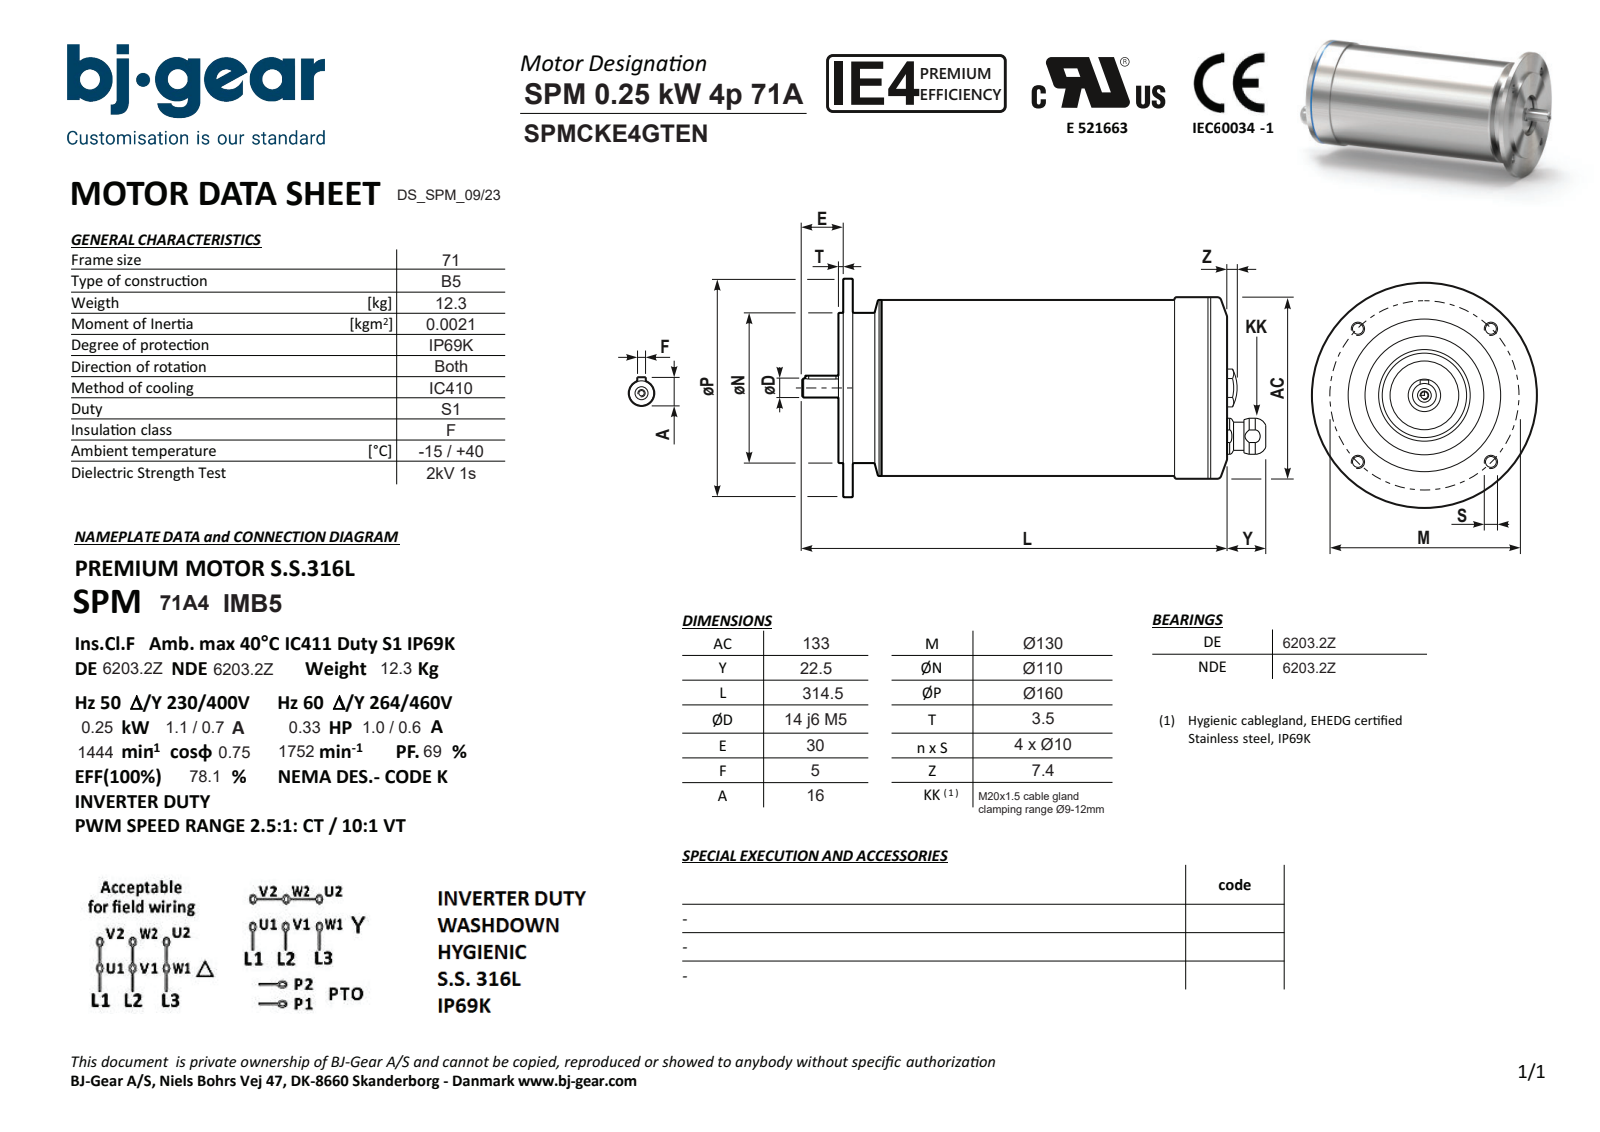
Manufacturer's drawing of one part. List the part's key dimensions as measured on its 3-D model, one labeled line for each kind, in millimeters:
Part name (STEP PRODUCT): SPMCKE4GTENN4KSA1-N---NNN
STEP written by: Solid Edge (AUTOMOTIVE_DESIGN)
Units: millimetres
Bodies: 1 solid, 86 faces (31 planar, 30 cylindrical, 25 other)
Overall size (bounding box): 341 × 160 × 160
Volume: 3 743 000 mm³ · Surface area: 167 199 mm²
Round holes (diameter × count): ⌀10 ×4, ⌀4.13 ×1, ⌀5.3 ×1, ⌀7 ×1, ⌀13.4 ×1, ⌀52 ×1
Round bosses / shafts (diameter × count): ⌀160 ×1, ⌀133 ×1, ⌀132.98 ×1, ⌀129 ×1, ⌀128.98 ×1, ⌀110 ×1, ⌀20 ×1, ⌀17 ×1
Partial cylindrical surfaces — rounded edges, fillets, slot ends (radius × count): R2.5 ×2, R12.8 ×1
Main face-to-face distances: 7, 276.5, 283.5, 287, 10.5, 3.5, 278, 1.5, 5.5, 9
Hole centre spacings: 65, 91.92, 47.49, 92.23, 129.99, 34
